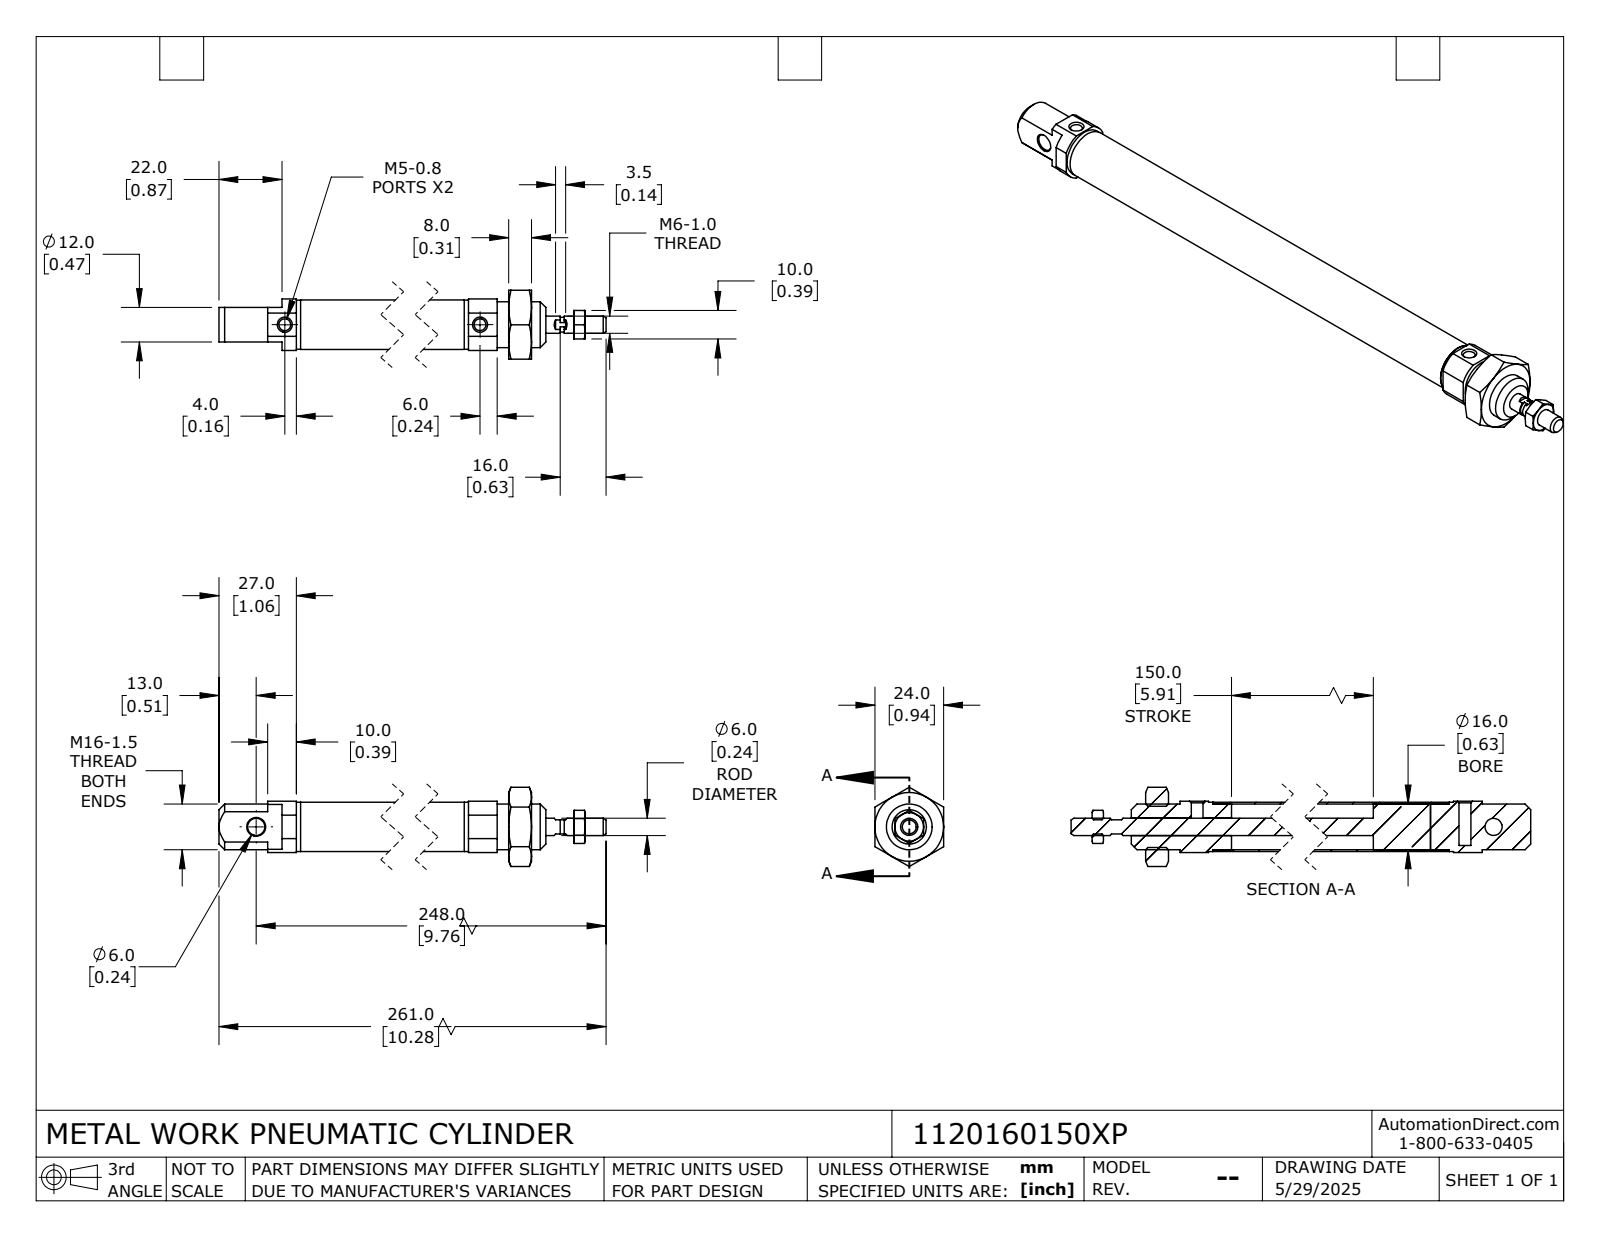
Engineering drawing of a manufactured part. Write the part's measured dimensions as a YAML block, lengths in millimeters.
part_name: "1120160150XP; 1120160150XP_BODY; 1120160150XP_ROD"
step_written_by: "SolidWorks 2024 (CONFIG_CONTROL_DESIGN)"
units: millimeters
bodies: {solids: 6, faces: 146, planar: 55, cylindrical: 45, other: 46}
overall_size: [261, 27.71, 24]
volume: 32070
surface_area: 32167
round_holes:
  - {diameter: 4.13, count: 2}
  - {diameter: 4.92, count: 1}
  - {diameter: 6, count: 1}
  - {diameter: 14.38, count: 1}
round_bosses_or_shafts:
  - {diameter: 17.27, count: 1}
  - {diameter: 17.2, count: 1}
  - {diameter: 16.15, count: 1}
  - {diameter: 16, count: 1}
  - {diameter: 6, count: 1}
  - {diameter: 5.2, count: 1}
partial_cylinders:
  - {radius: 9.85, count: 1}
face_to_face_distances: [8, 18, 24, 22, 200, 12, 205, 17, 192, 2.97]
hole_center_spacings: [194]
